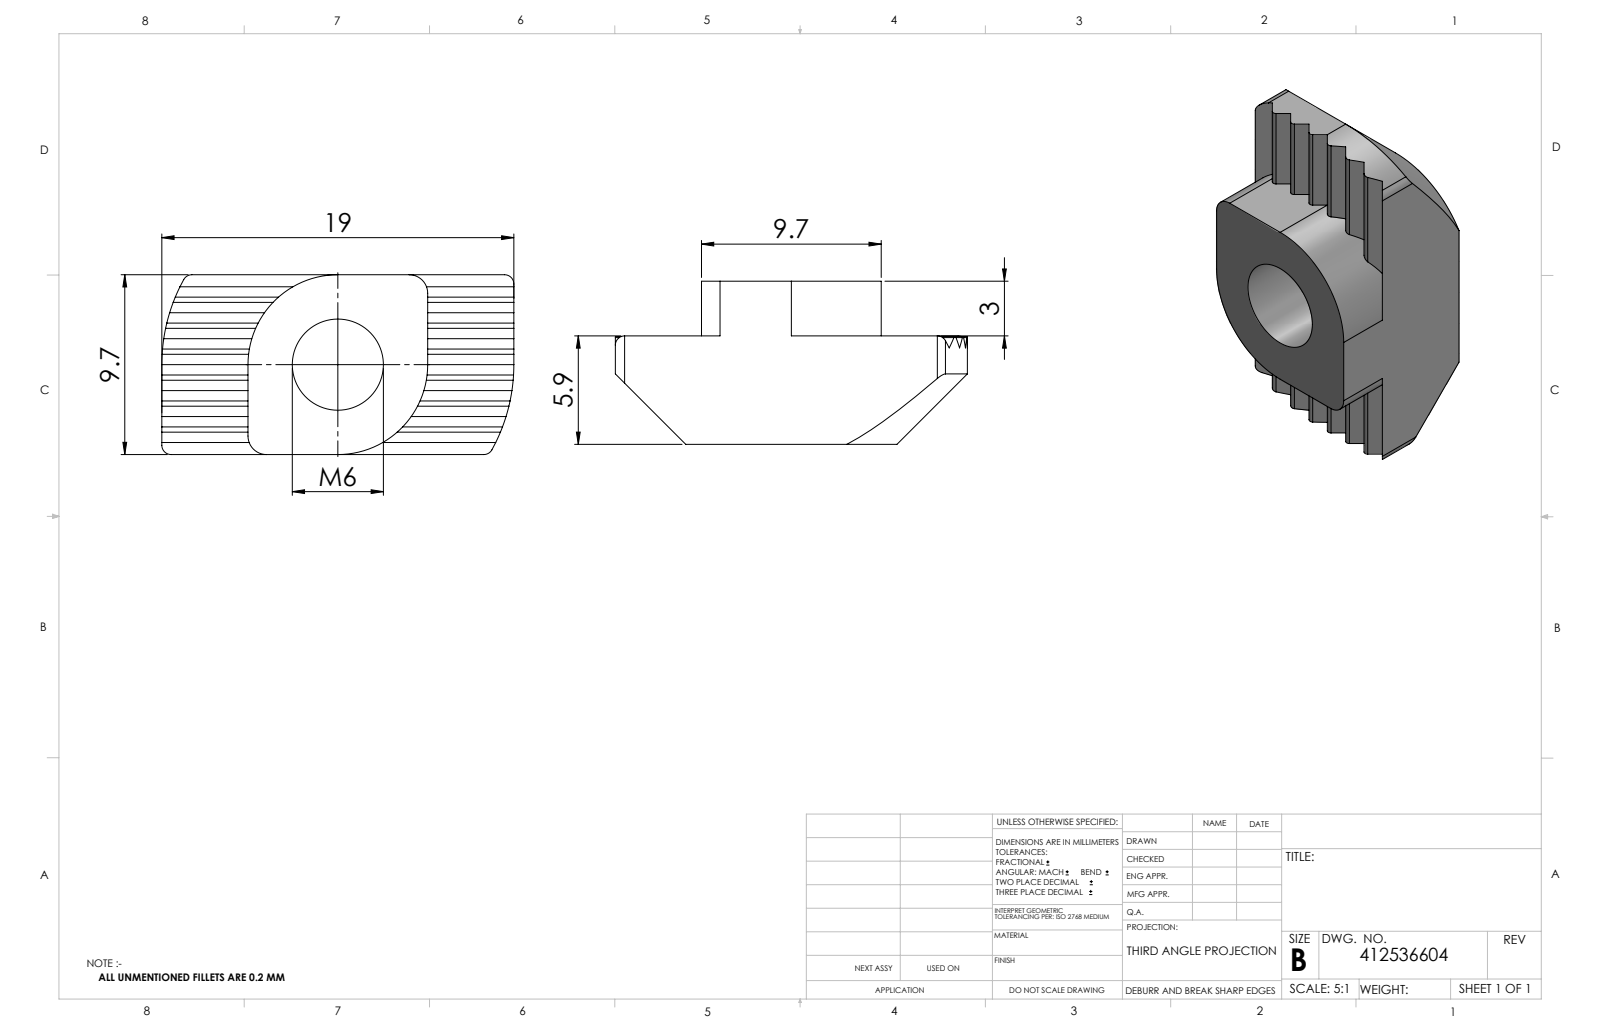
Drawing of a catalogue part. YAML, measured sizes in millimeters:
part_name: "412536604_c_1"
step_written_by: "SolidWorks 2014 (CONFIG_CONTROL_DESIGN)"
units: millimeters
bodies: {solids: 1, faces: 64, planar: 38, cylindrical: 24, other: 2}
overall_size: [19, 9.7, 8.8]
volume: 958
surface_area: 839
round_holes:
  - {diameter: 4.92, count: 1}
partial_cylinders:
  - {radius: 0.2, count: 6}
  - {radius: 0.5, count: 4}
  - {radius: 1, count: 2}
  - {radius: 4.85, count: 1}
  - {radius: 9.5, count: 1}
face_to_face_distances: [9.7, 0.99, 1.98, 8.8, 2.97, 3.96, 4.95, 5.94, 4.65, 14.35]
